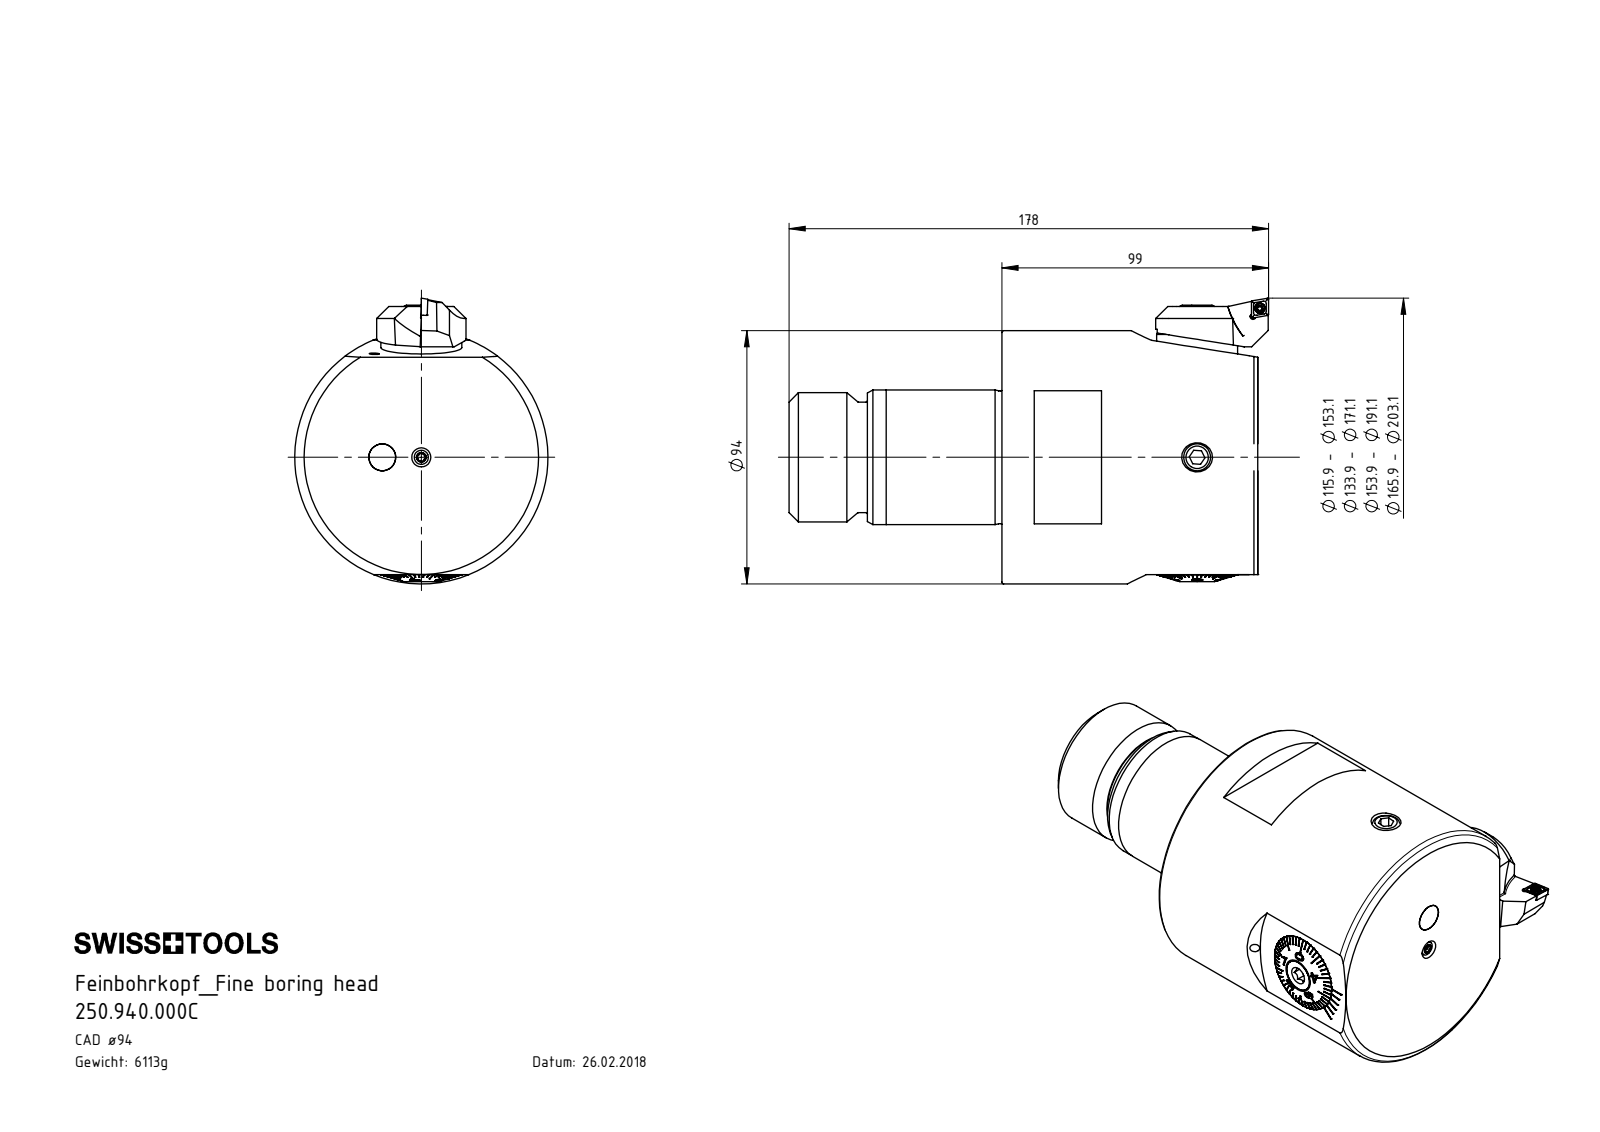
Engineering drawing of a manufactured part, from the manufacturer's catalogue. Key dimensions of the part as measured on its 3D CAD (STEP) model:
Part name (STEP PRODUCT): Klebstoff D10; ISO 4026 - M10 x 28; A55-BG3.011.033_A_gekrzt; CA9-F94.K20.099_A (+8 more)
STEP written by: SolidWorks 2017 (CONFIG_CONTROL_DESIGN)
Units: millimetres
Bodies: 18 solids, 858 faces (344 planar, 178 cylindrical, 336 other)
Overall size (bounding box): 178 × 106.03 × 94
Volume: 779 119 mm³ · Surface area: 94 177 mm²
Round holes (diameter × count): ⌀3.3 ×7, ⌀8.5 ×3, ⌀2.05 ×1, ⌀2.1 ×1, ⌀2.8 ×1, ⌀3.85 ×1, ⌀4.2 ×1, ⌀5 ×1, ⌀8 ×1, ⌀10 ×1, ⌀11 ×1, ⌀11.75 ×1
Round bosses / shafts (diameter × count): ⌀10 ×2, ⌀94 ×1, ⌀50 ×1, ⌀49.95 ×1, ⌀49.3 ×1, ⌀48 ×1, ⌀41 ×1, ⌀29.98 ×1
Partial cylindrical surfaces — rounded edges, fillets, slot ends (radius × count): R0.21 ×6, R0.34 ×6, R0.59 ×6, R0.36 ×5, R0.5 ×4, R3.2 ×3, R10 ×2, R0.36 ×1
Main face-to-face distances: 95, 80, 79, 174, 89.53, 2.5, 12, 81.6, 7.93, 88.35
Hole centre spacings: 3.91, 4.04, 14.5, 22.54, 32.5, 35
